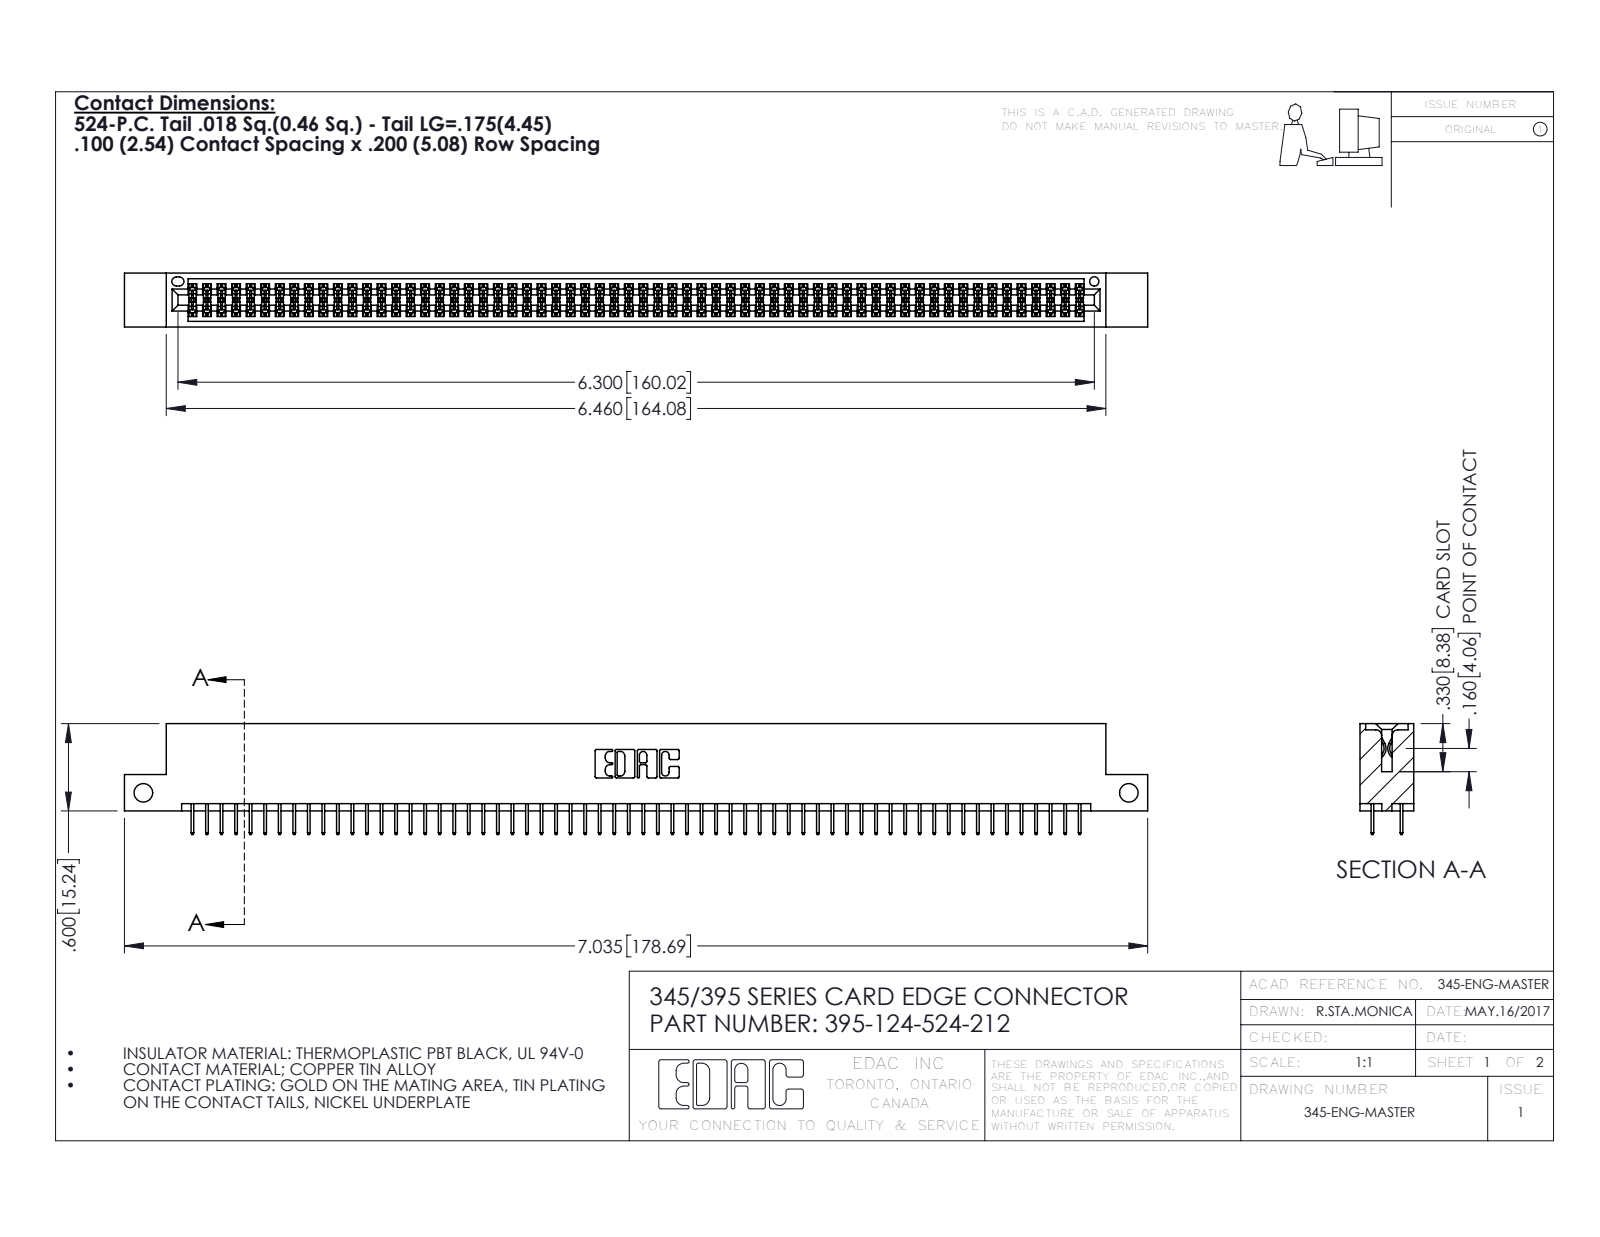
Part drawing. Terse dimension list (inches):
name: 395-124-524-212; 345 Part_Flush Mounting Lugs - Side Mount; 345-292-001_345-293-124
written by: SolidWorks 2016 (CONFIG_CONTROL_DESIGN)
unit: in
bodies: 125 solids, 6822 faces (4916 planar, 1906 cylindrical, 0 other)
size: 7.035 × 0.762 × 0.37
volume: 1.054 in³; area: 39.19 in²
holes: 2× ⌀0.128, 1× ⌀0.064
rounds: 186× R0.006, 22× R0.01, 6× R0.007, 6× R0.031, 3× R0.026, 2× R0.014, 2× R0.019, 2× R0.022
face distances: 0.072, 0.298, 0.2, 0.37, 0.098, 0.272, 0.025, 0.225, 0.072, 0.175
hole spacings: 6.775
